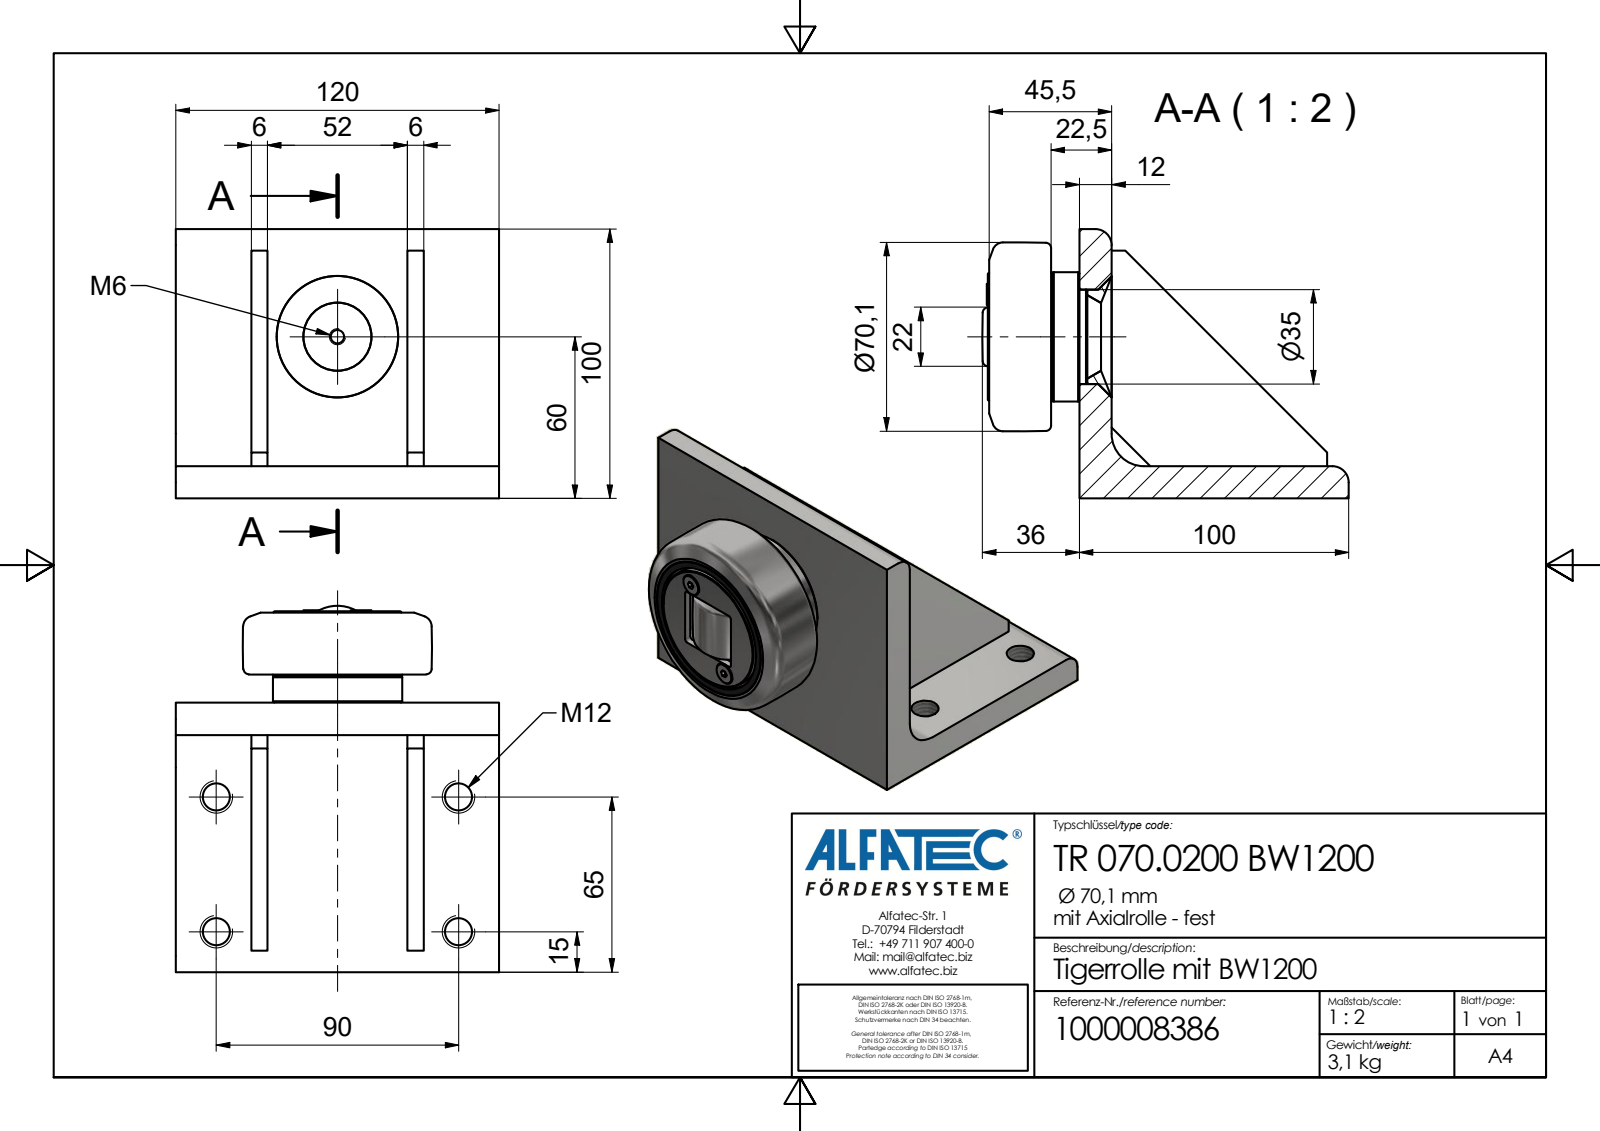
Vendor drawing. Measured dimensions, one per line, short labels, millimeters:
name: TR 070.0200 BW1200_Kontur
written by: Autodesk Inventor 2020 (AP242_MANAGED_MODEL_BASED_3D_ENGINEERING_MIM_LF)
unit: mm
bodies: 1 solid, 81 faces (50 planar, 18 cylindrical, 13 other)
size: 136 × 120 × 100
volume: 412 975 mm³; area: 76 896 mm²
holes: 4× ⌀10.11, 1× ⌀2.5, 1× ⌀4.92
bosses: 2× ⌀7.8, 1× ⌀48, 1× ⌀47.3
rounds: 4× R1, 2× R6, 1× R12
face distances: 12, 6, 58, 34, 92, 28, 86, 64, 52, 120
hole spacings: 50, 90, 102.96
